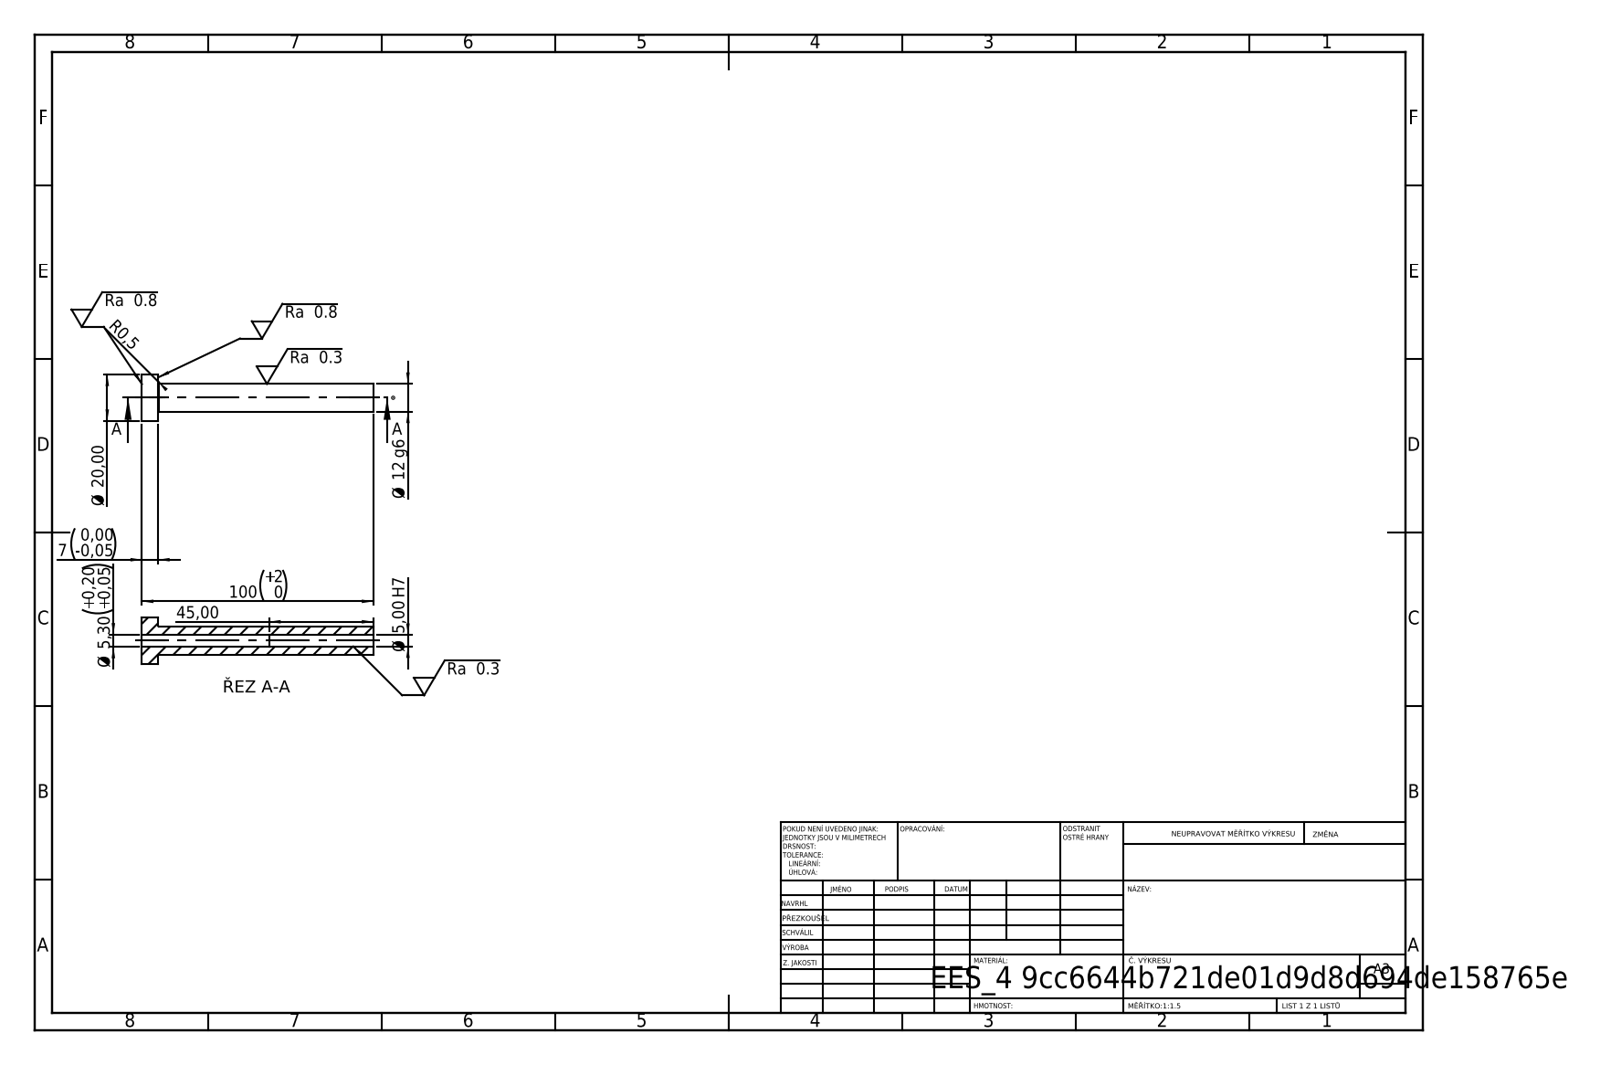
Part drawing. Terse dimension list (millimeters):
written by: SolidWorks 2019 (CONFIG_CONTROL_DESIGN)
unit: mm
bodies: 1 solid, 14 faces (4 planar, 8 cylindrical, 2 other)
size: 100 × 20 × 20
volume: 10 622 mm³; area: 6 150 mm²
holes: 1× ⌀5, 1× ⌀5.3
bosses: 1× ⌀20, 1× ⌀12
face distances: 7, 100, 93, 55, 48, 45
